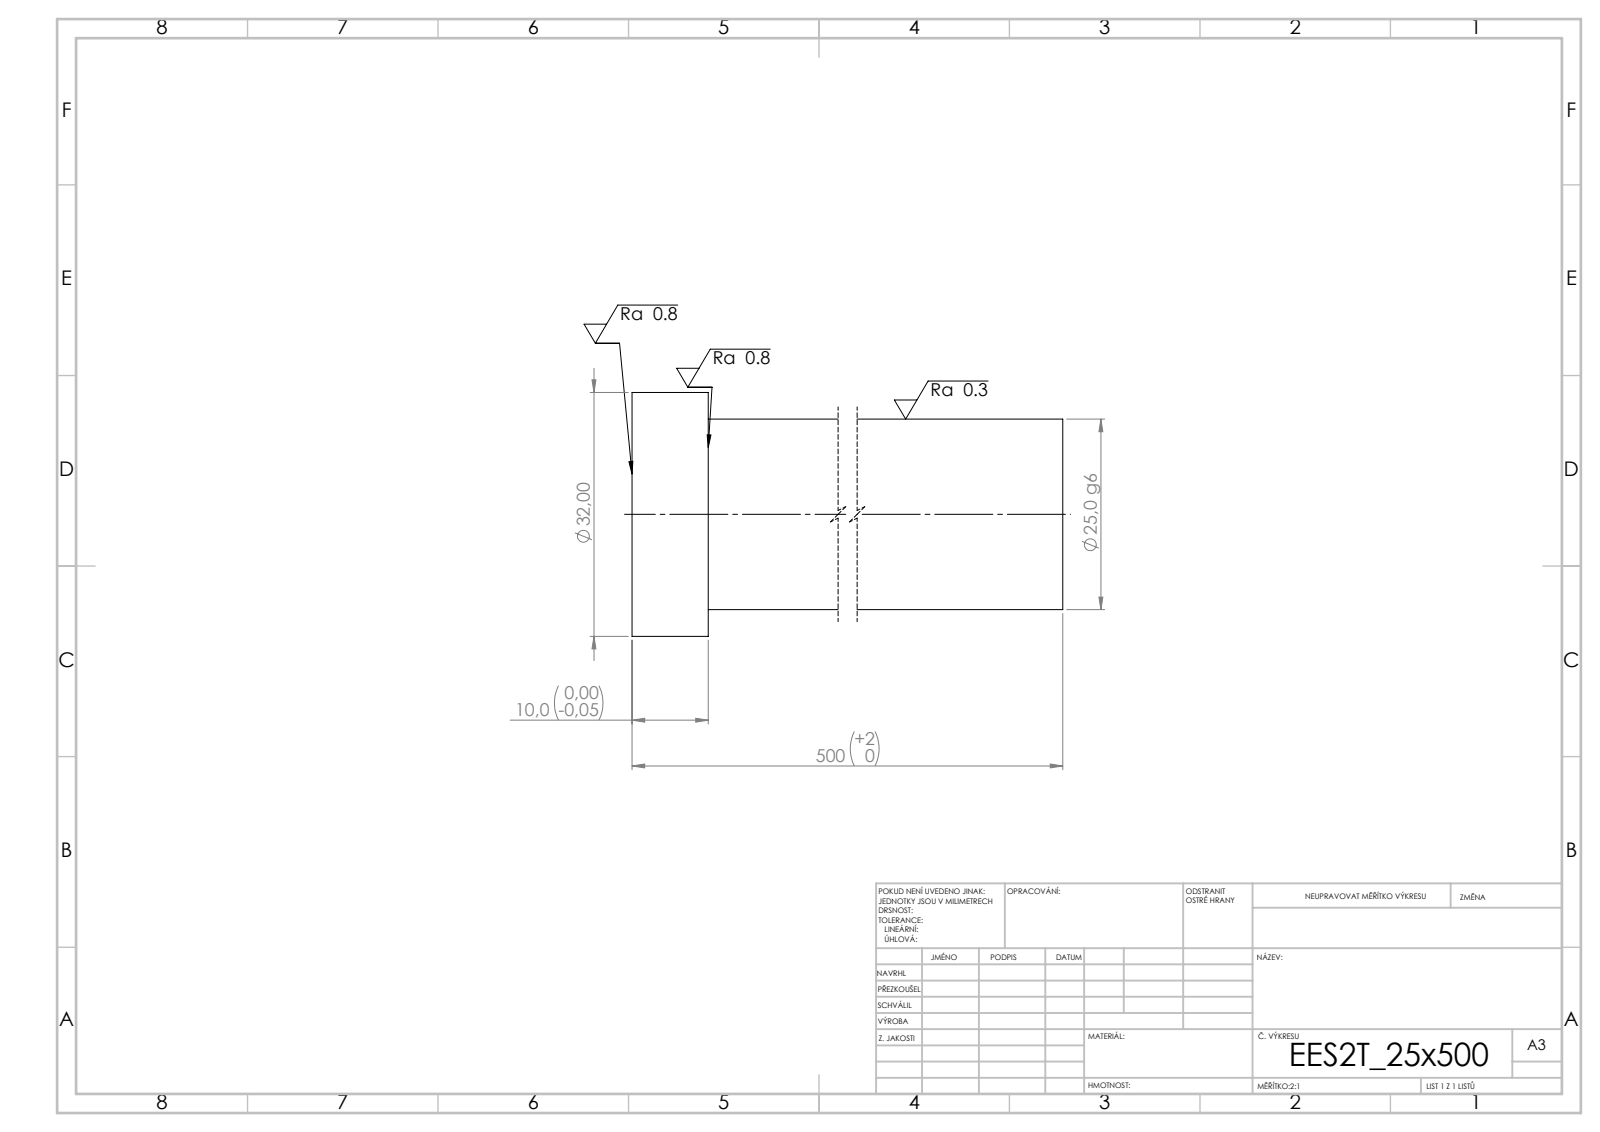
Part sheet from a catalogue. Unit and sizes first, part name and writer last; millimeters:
Units: millimetres
Overall size (bounding box): 500 × 32 × 32
Round bosses / shafts (diameter × count): ⌀32 ×1, ⌀25 ×1
Main face-to-face distances: 500, 10, 490
Volume: 248 571 mm³ · Surface area: 41 098 mm²
Bodies: 1 solid, 7 faces (3 planar, 4 cylindrical, 0 other)
STEP written by: SolidWorks 2019 (CONFIG_CONTROL_DESIGN)
